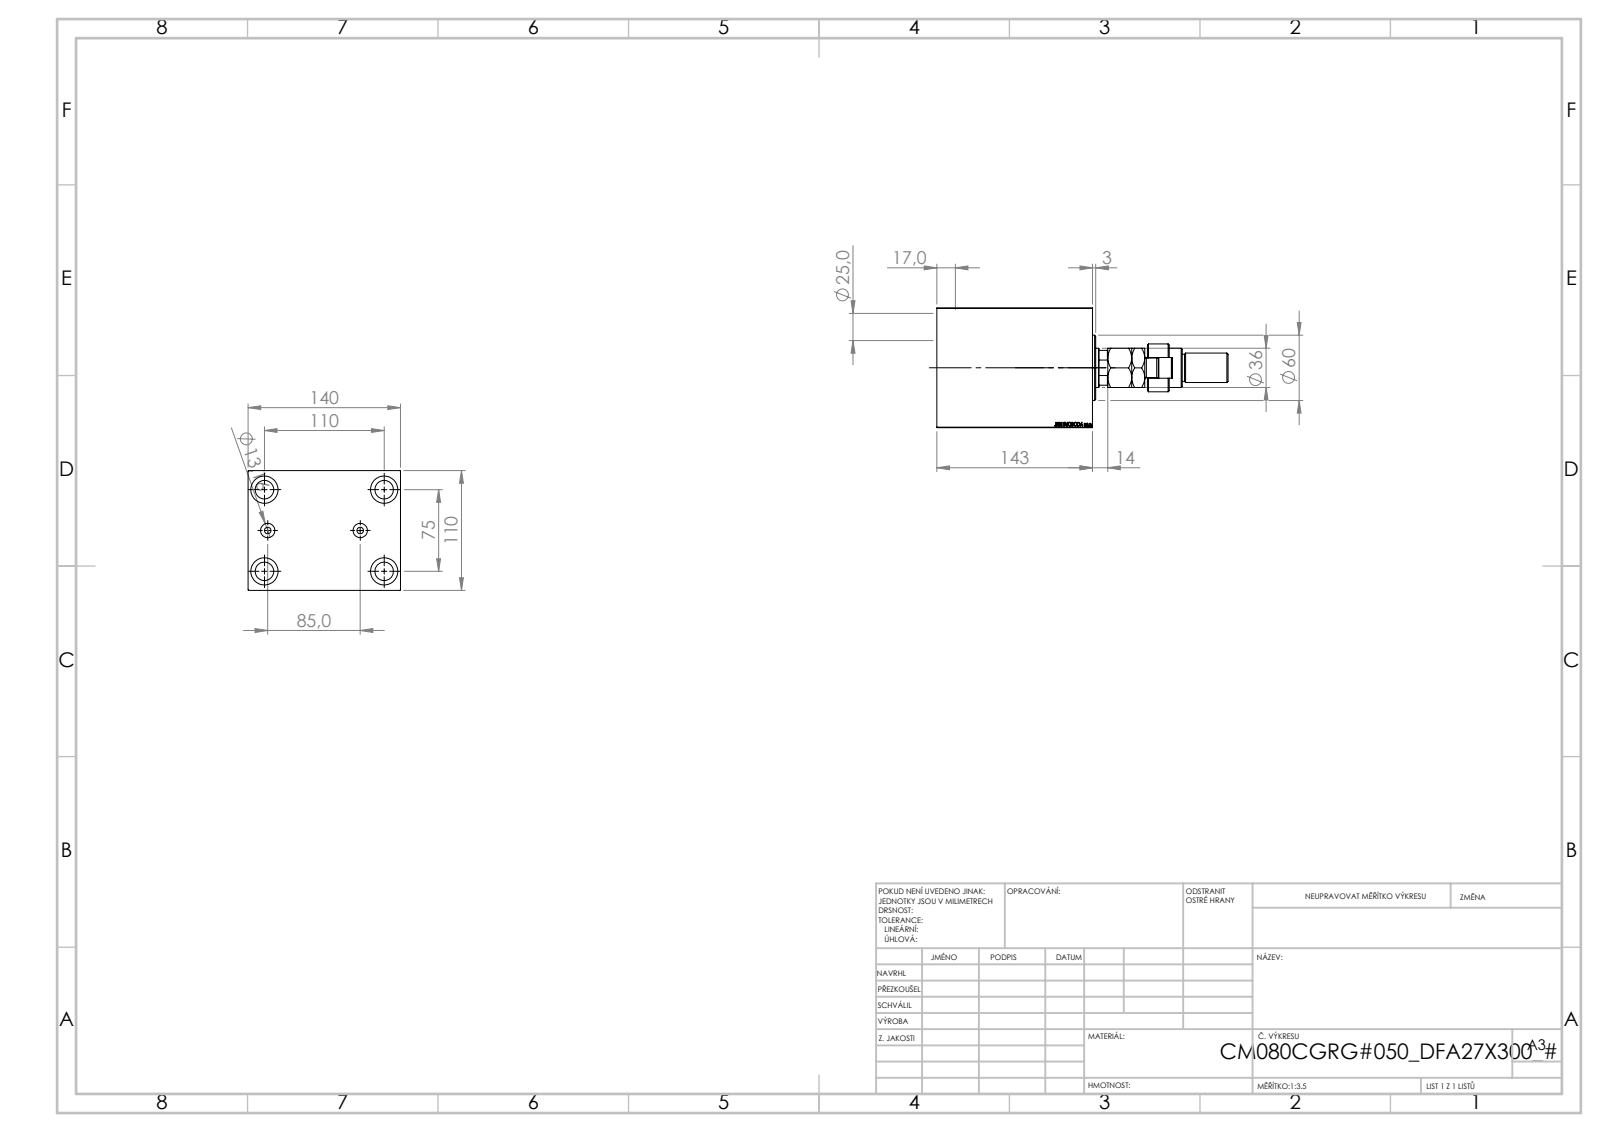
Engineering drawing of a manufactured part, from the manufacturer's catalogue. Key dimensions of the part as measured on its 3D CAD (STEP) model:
Part name (STEP PRODUCT): V450CM_C_Body; V450CM_C_VCP; V450CM_VC_B; MFA (+1 more)
STEP written by: SolidWorks 2019 (CONFIG_CONTROL_DESIGN)
Units: millimetres
Bodies: 5 solids, 948 faces (439 planar, 71 cylindrical, 438 other)
Overall size (bounding box): 267.5 × 140 × 110
Volume: 1 925 000 mm³ · Surface area: 224 665 mm²
Round holes (diameter × count): ⌀17 ×4, ⌀25 ×4, ⌀6 ×2, ⌀13.16 ×2, ⌀25.5 ×1, ⌀39.5 ×1, ⌀80 ×1, ⌀82 ×1, ⌀87 ×1
Round bosses / shafts (diameter × count): ⌀60 ×1, ⌀44 ×1, ⌀36 ×1, ⌀28 ×1, ⌀27 ×1, ⌀25 ×1, ⌀18 ×1
Partial cylindrical surfaces — rounded edges, fillets, slot ends (radius × count): R9.5 ×1, R15 ×1, R17.5 ×1
Main face-to-face distances: 110, 140, 143, 88.25, 54.75, 10, 133, 83, 78.25, 60
Hole centre spacings: 39.53, 66.57, 104.46, 42.5, 75, 110, 133.14, 85
